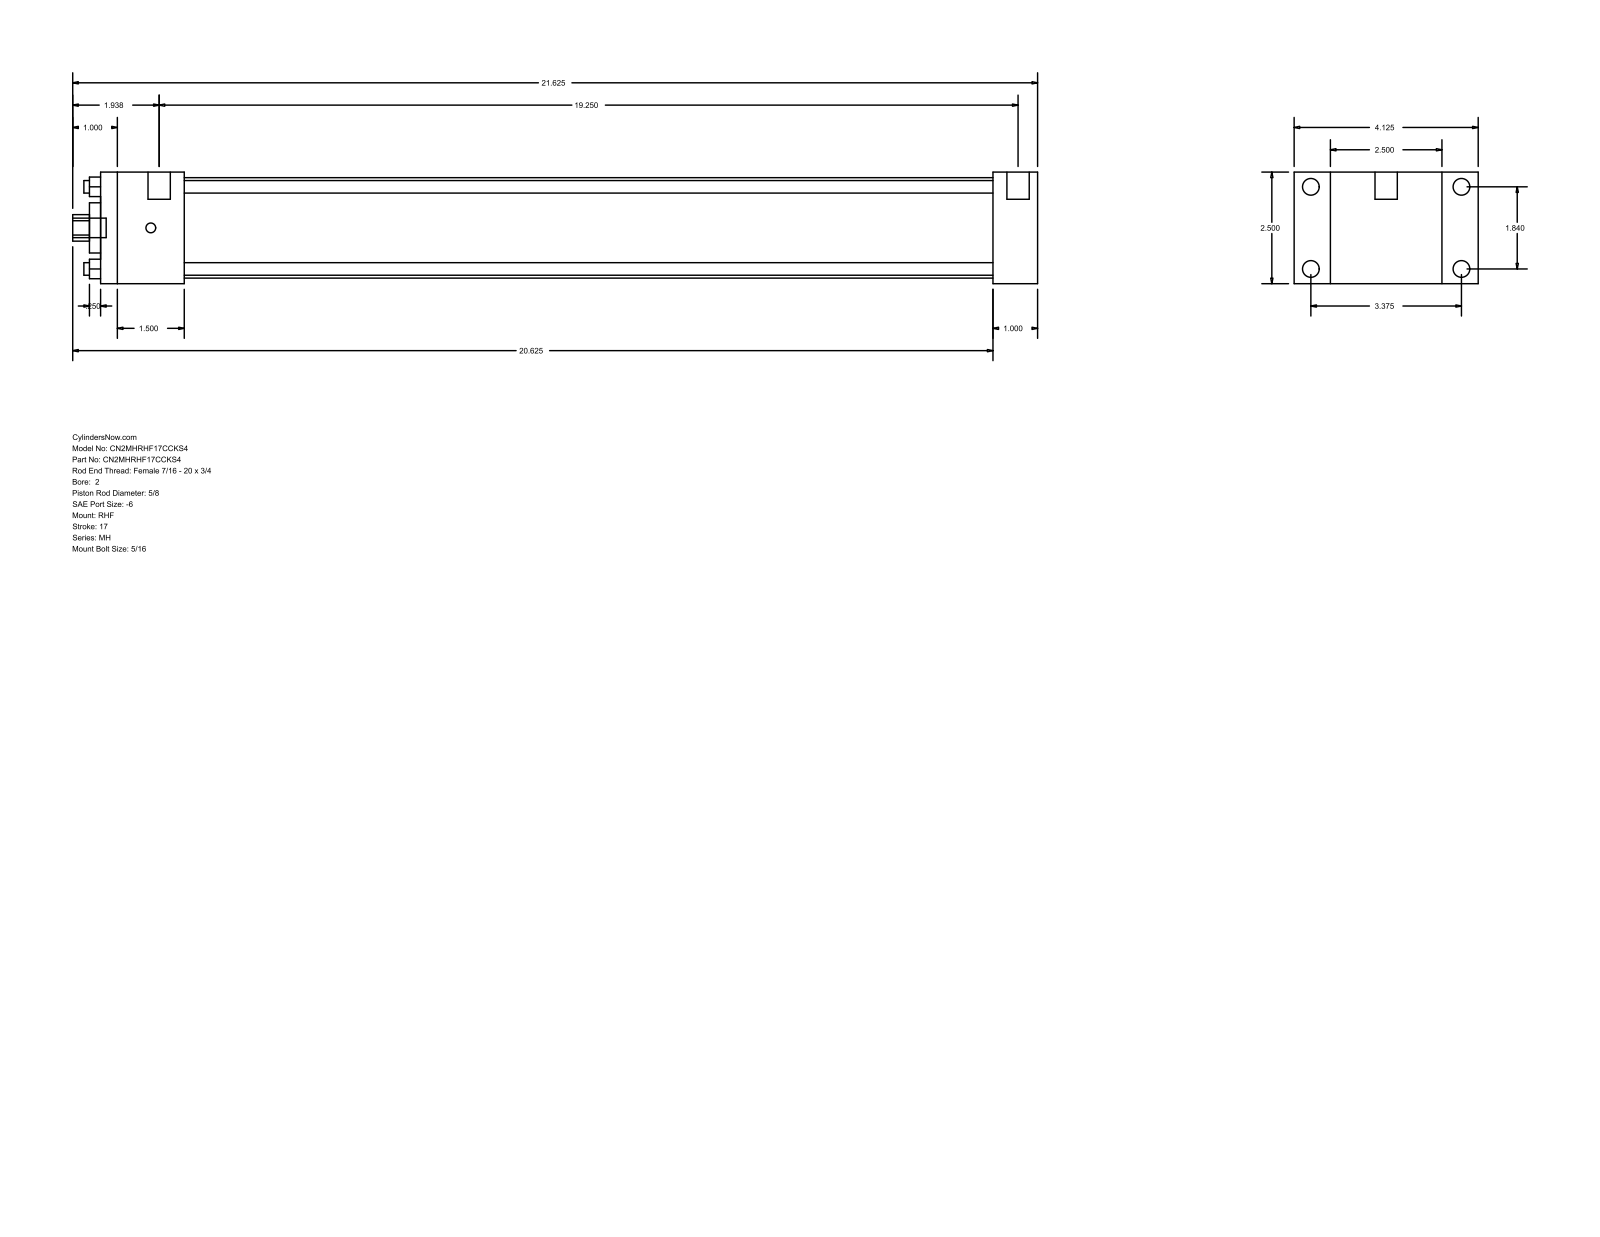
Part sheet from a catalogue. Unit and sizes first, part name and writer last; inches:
Units: inches
Overall size (bounding box): 21.625 × 4.125 × 2.5
Round holes (diameter × count): ⌀0.281 ×4, ⌀0.625 ×1, ⌀1.125 ×1, ⌀2.25 ×1
Round bosses / shafts (diameter × count): ⌀0.375 ×4, ⌀0.219 ×4, ⌀0.5 ×2, ⌀0.437 ×1
Partial cylindrical surfaces — rounded edges, fillets, slot ends (radius × count): R0.297 ×1
Main face-to-face distances: 2.5, 1, 0.813, 3.313, 20, 21, 4.125, 1.875, 18.125, 19.125
Hole centre spacings: 1.301, 1.84, 2.602
Bodies: 0 solids, 88 faces (60 planar, 28 cylindrical, 0 other)
Part name (STEP PRODUCT): MH_RHF__0200_0.625
STEP written by: GSSL Pune (CONFIG_CONTROL_DESIGN)
